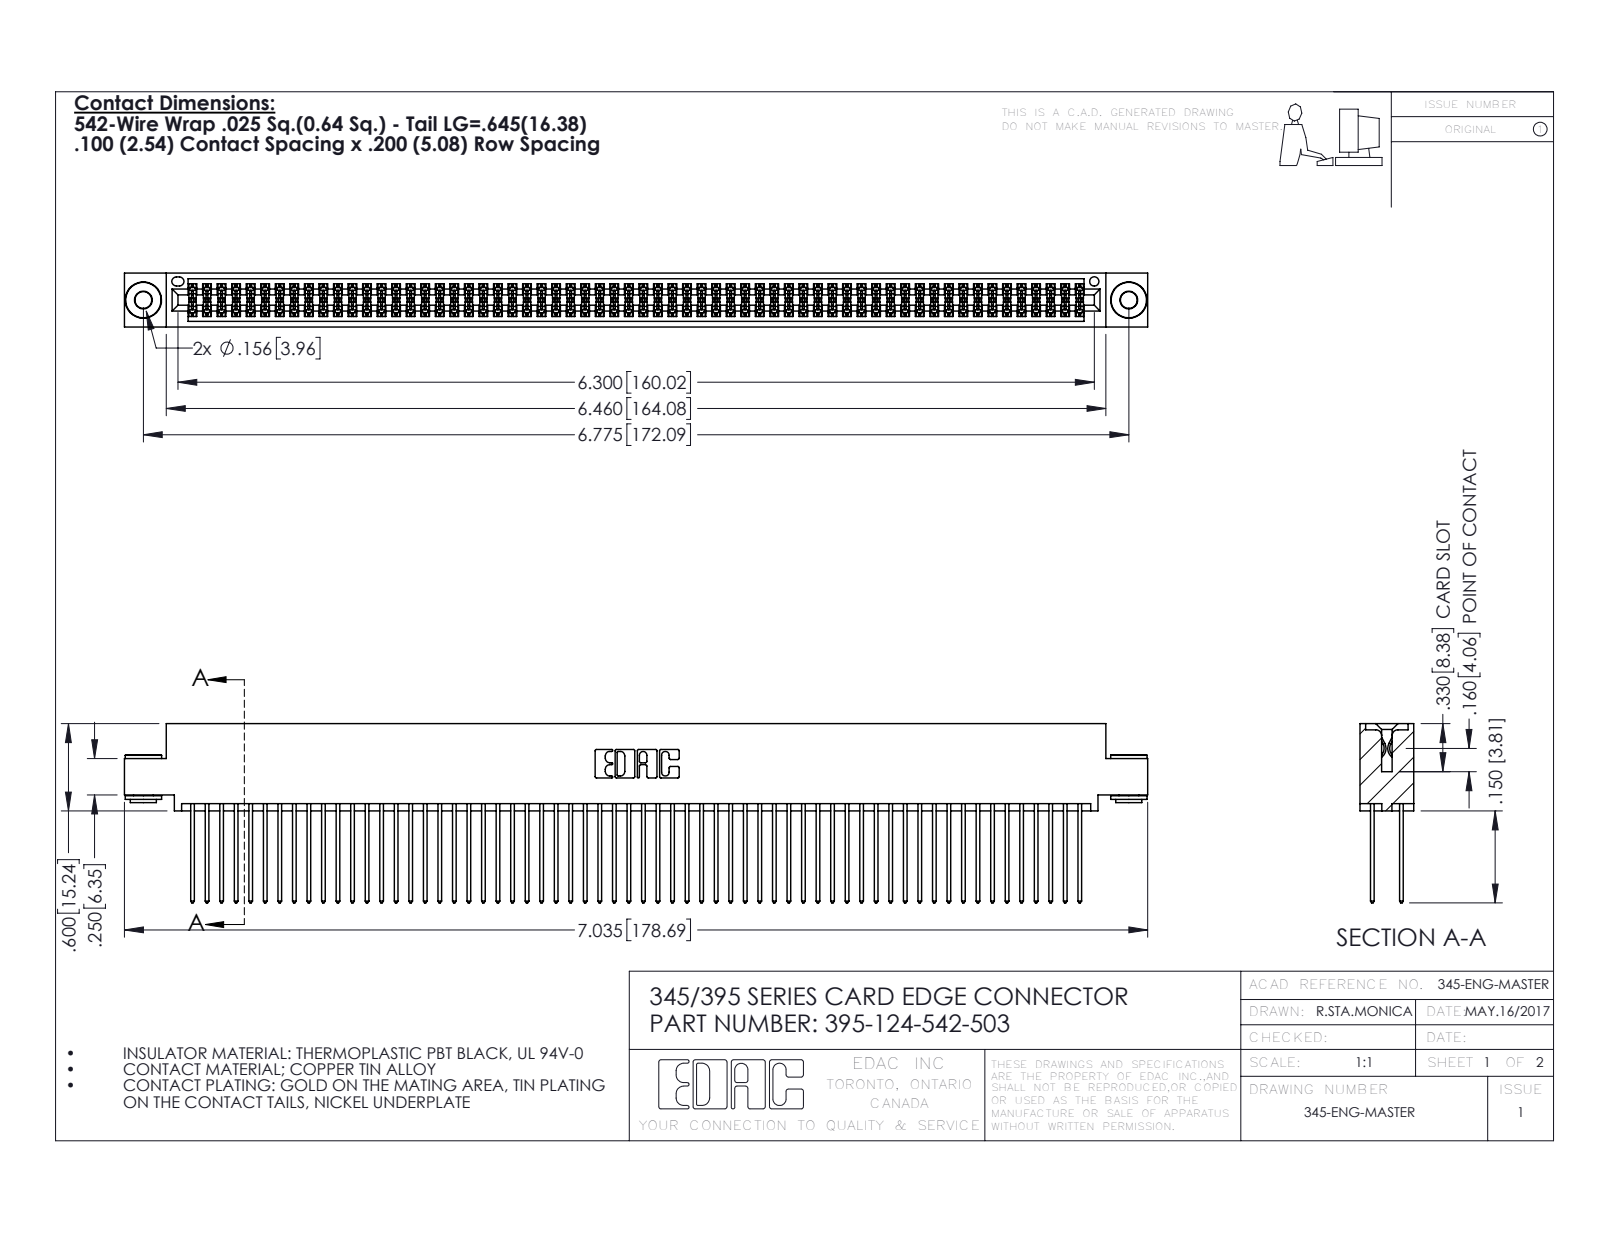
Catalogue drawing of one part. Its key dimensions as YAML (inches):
part_name: "395-124-542-503; 345 Part_0.110 Offset - 0.156 Dia-TH; 345-250-002_345-250-002-102; 345-292-001_345-293-142"
step_written_by: "SolidWorks 2016 (CONFIG_CONTROL_DESIGN)"
units: inches
bodies: {solids: 127, faces: 6368, planar: 4186, cylindrical: 2174, other: 8}
overall_size: [7.035, 1.232, 0.37]
volume: 1.103
surface_area: 46.65
round_holes:
  - {diameter: 0.116, count: 2}
  - {diameter: 0.156, count: 2}
  - {diameter: 0.064, count: 1}
round_bosses_or_shafts:
  - {diameter: 0.25, count: 2}
  - {diameter: 0.18, count: 2}
  - {diameter: 0.136, count: 2}
partial_cylinders:
  - {radius: 0.006, count: 186}
  - {radius: 0.01, count: 124}
  - {radius: 0.01, count: 22}
  - {radius: 0.007, count: 6}
  - {radius: 0.031, count: 6}
  - {radius: 0.026, count: 3}
  - {radius: 0.014, count: 2}
  - {radius: 0.019, count: 2}
face_to_face_distances: [0.072, 0.298, 0.2, 0.025, 0.098, 0.272, 0.225, 0.37, 0.175, 0.149]
hole_center_spacings: [0.27, 6.539, 6.775]
